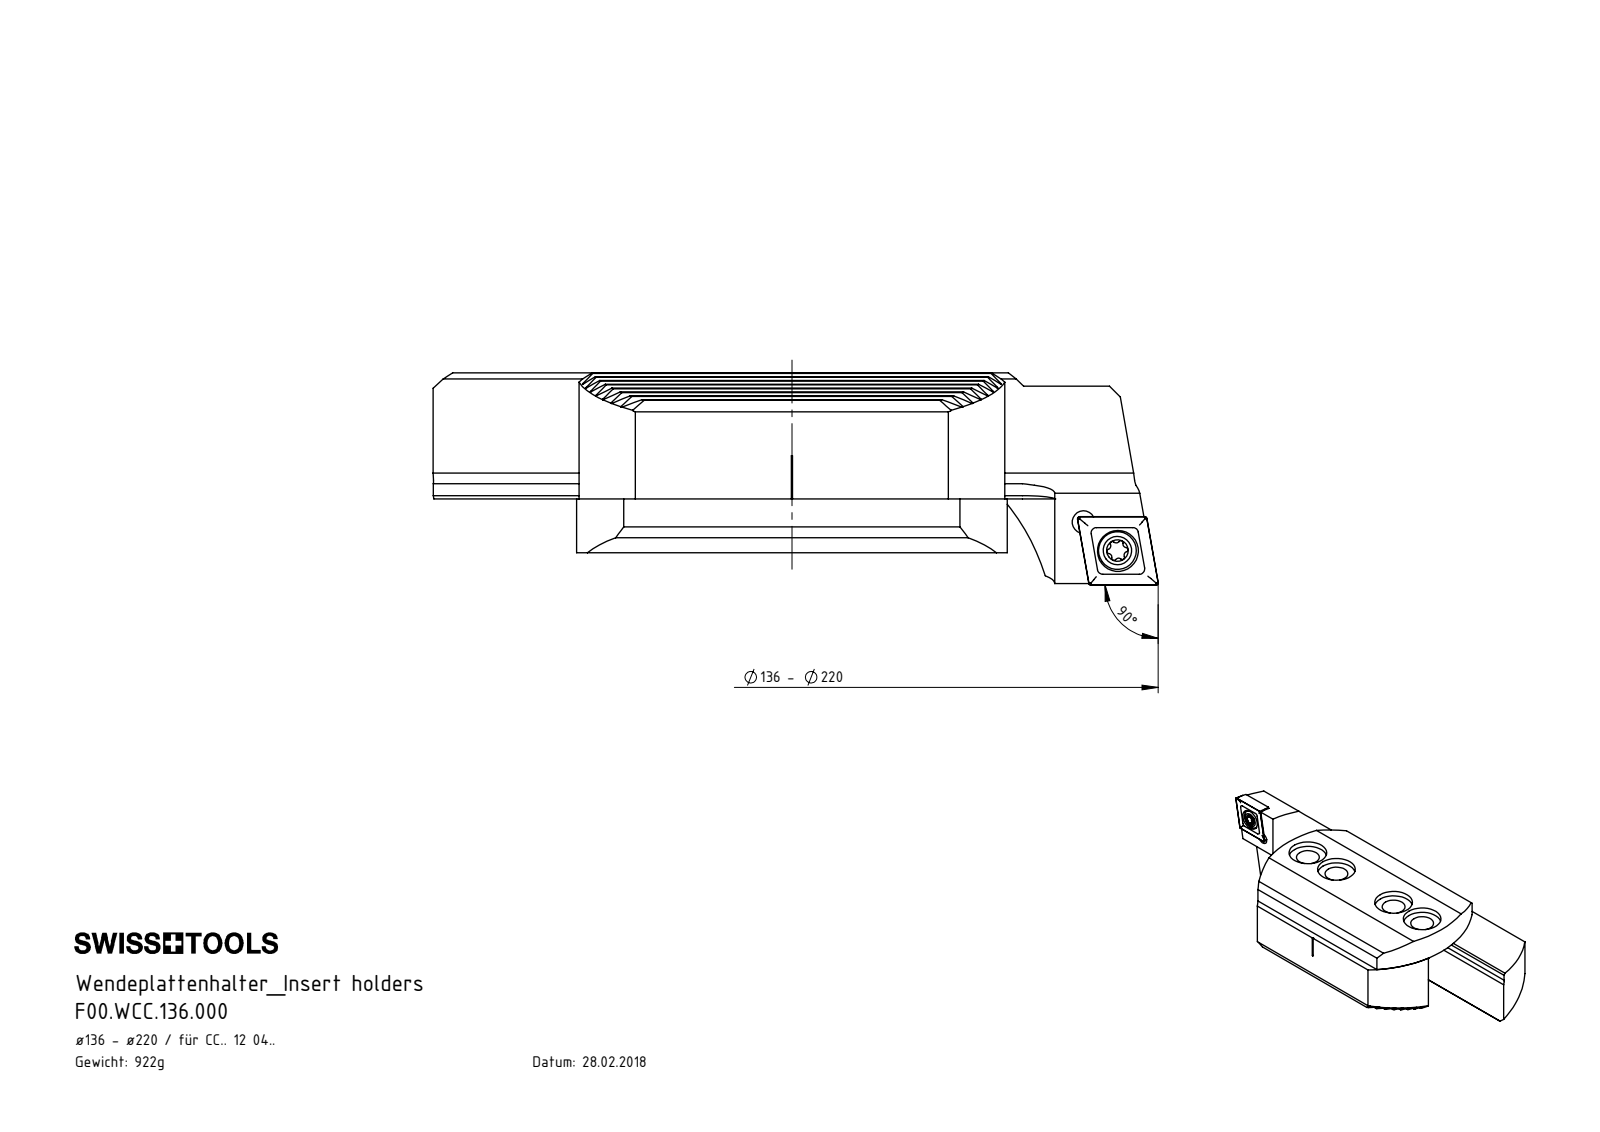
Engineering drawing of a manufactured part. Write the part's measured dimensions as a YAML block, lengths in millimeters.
part_name: "F00-WCB.136.002_A; F00-WCB.136.003_A; F00-WCC.136.001; F00-WCC.136.001_C (+3 more)"
step_written_by: "SolidWorks 2017 (CONFIG_CONTROL_DESIGN)"
units: millimeters
bodies: {solids: 5, faces: 632, planar: 382, cylindrical: 68, other: 182}
overall_size: [134.59, 55, 39.4]
volume: 117488
surface_area: 32184
round_holes:
  - {diameter: 8.5, count: 4}
  - {diameter: 14, count: 4}
  - {diameter: 4.2, count: 2}
  - {diameter: 5.5, count: 1}
  - {diameter: 7.6, count: 1}
round_bosses_or_shafts:
  - {diameter: 7, count: 1}
  - {diameter: 5, count: 1}
partial_cylinders:
  - {radius: 0.2, count: 16}
  - {radius: 0.39, count: 6}
  - {radius: 40, count: 6}
  - {radius: 0.69, count: 4}
  - {radius: 0.69, count: 2}
  - {radius: 0.8, count: 1}
  - {radius: 6, count: 1}
face_to_face_distances: [2.38, 4.76, 21.3, 33.7, 7.14, 12.4, 9.52, 10, 4.77, 7.15]
hole_center_spacings: [15, 45, 8.21, 8.33, 30, 60]
